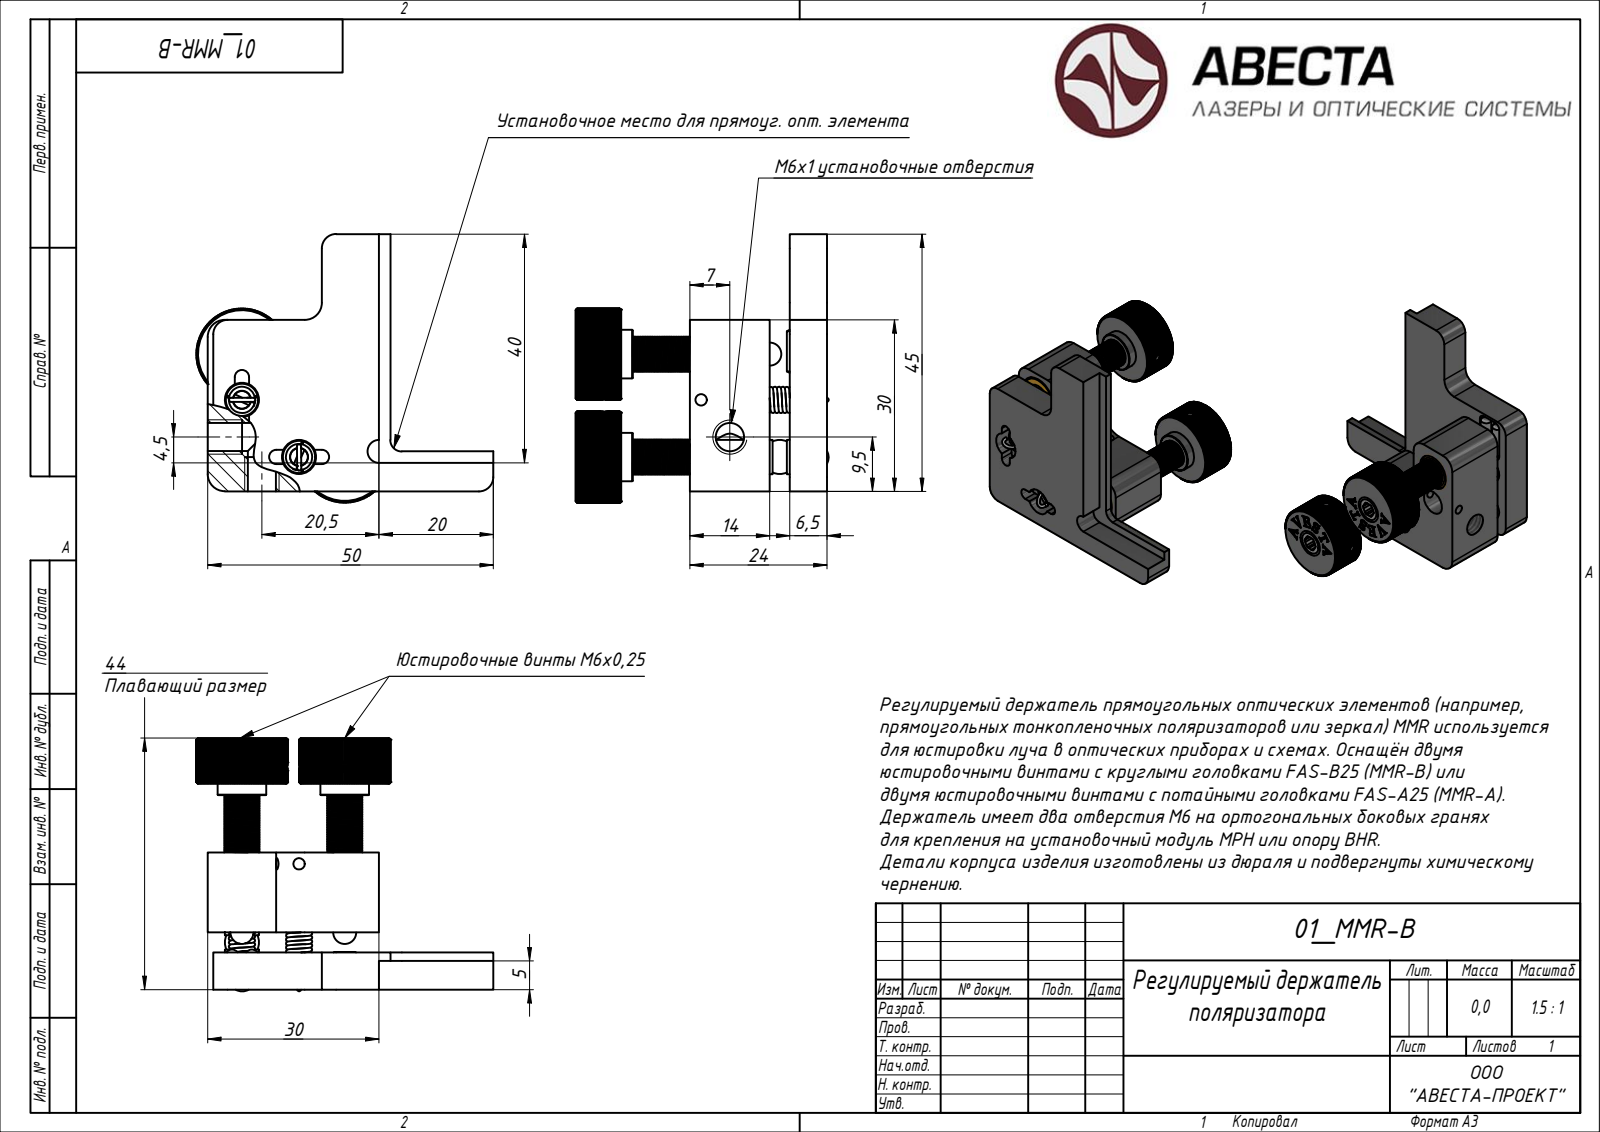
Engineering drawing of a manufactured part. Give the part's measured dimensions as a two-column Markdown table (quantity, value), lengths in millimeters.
| quantity | value |
| --- | --- |
| STEP written by | ST-DEVELOPER v15 (AUTOMOTIVE_DESIGN) |
| units | millimeters |
| bodies | 14 solids, 605 faces (285 planar, 0 cylindrical, 320 other) |
| overall size | 52 × 47 × 40.6 |
| volume | 17 809 mm³ |
| surface area | 13 413 mm² |
| main face-to-face distances | 6.5, 10, 3.5, 30, 12, 24, 17.5, 14, 8, 5 |
